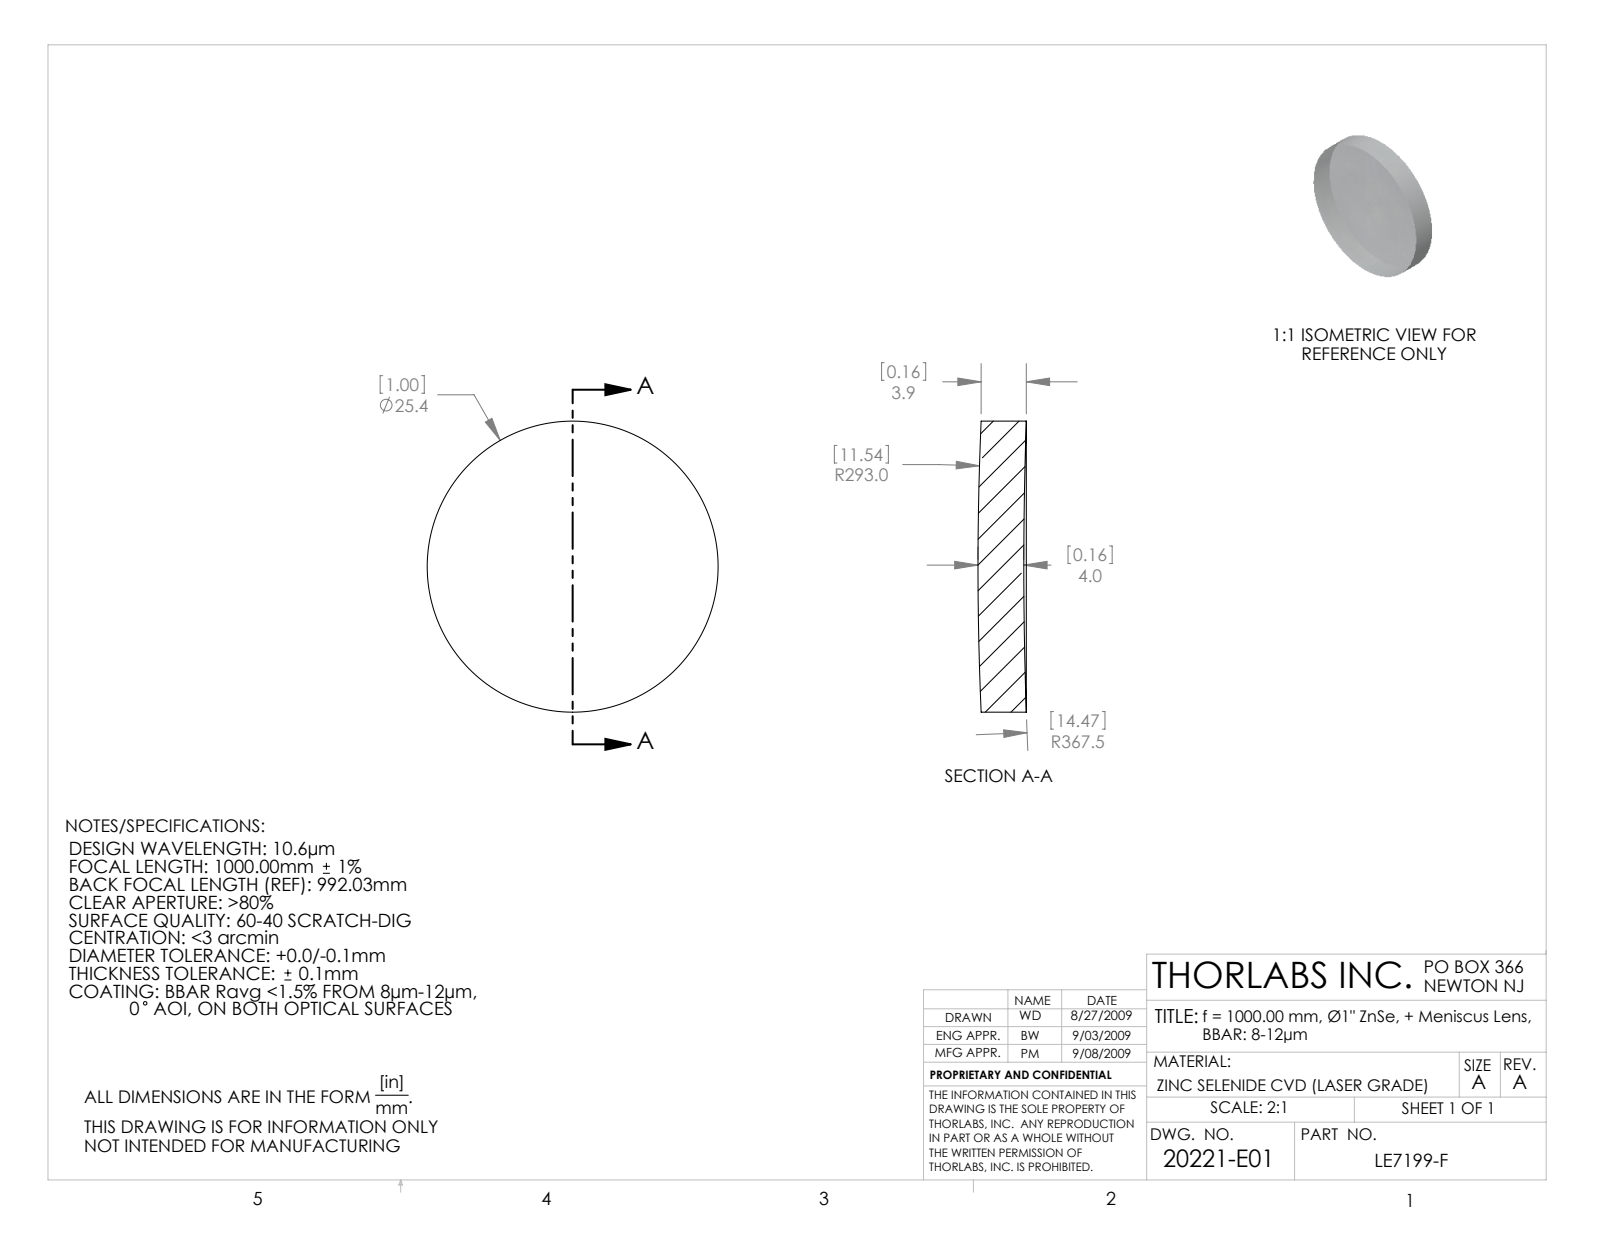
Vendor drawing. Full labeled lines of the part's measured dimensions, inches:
Part name (STEP PRODUCT): 20221-E0W
STEP written by: SolidWorks 2007 (CONFIG_CONTROL_DESIGN)
Units: inches
Bodies: 1 solid, 6 faces (0 planar, 2 cylindrical, 4 other)
Overall size (bounding box): 1 × 1 × 0.166
Volume: 0.123 in³ · Surface area: 2.06 in²
Round bosses / shafts (diameter × count): ⌀1 ×1
